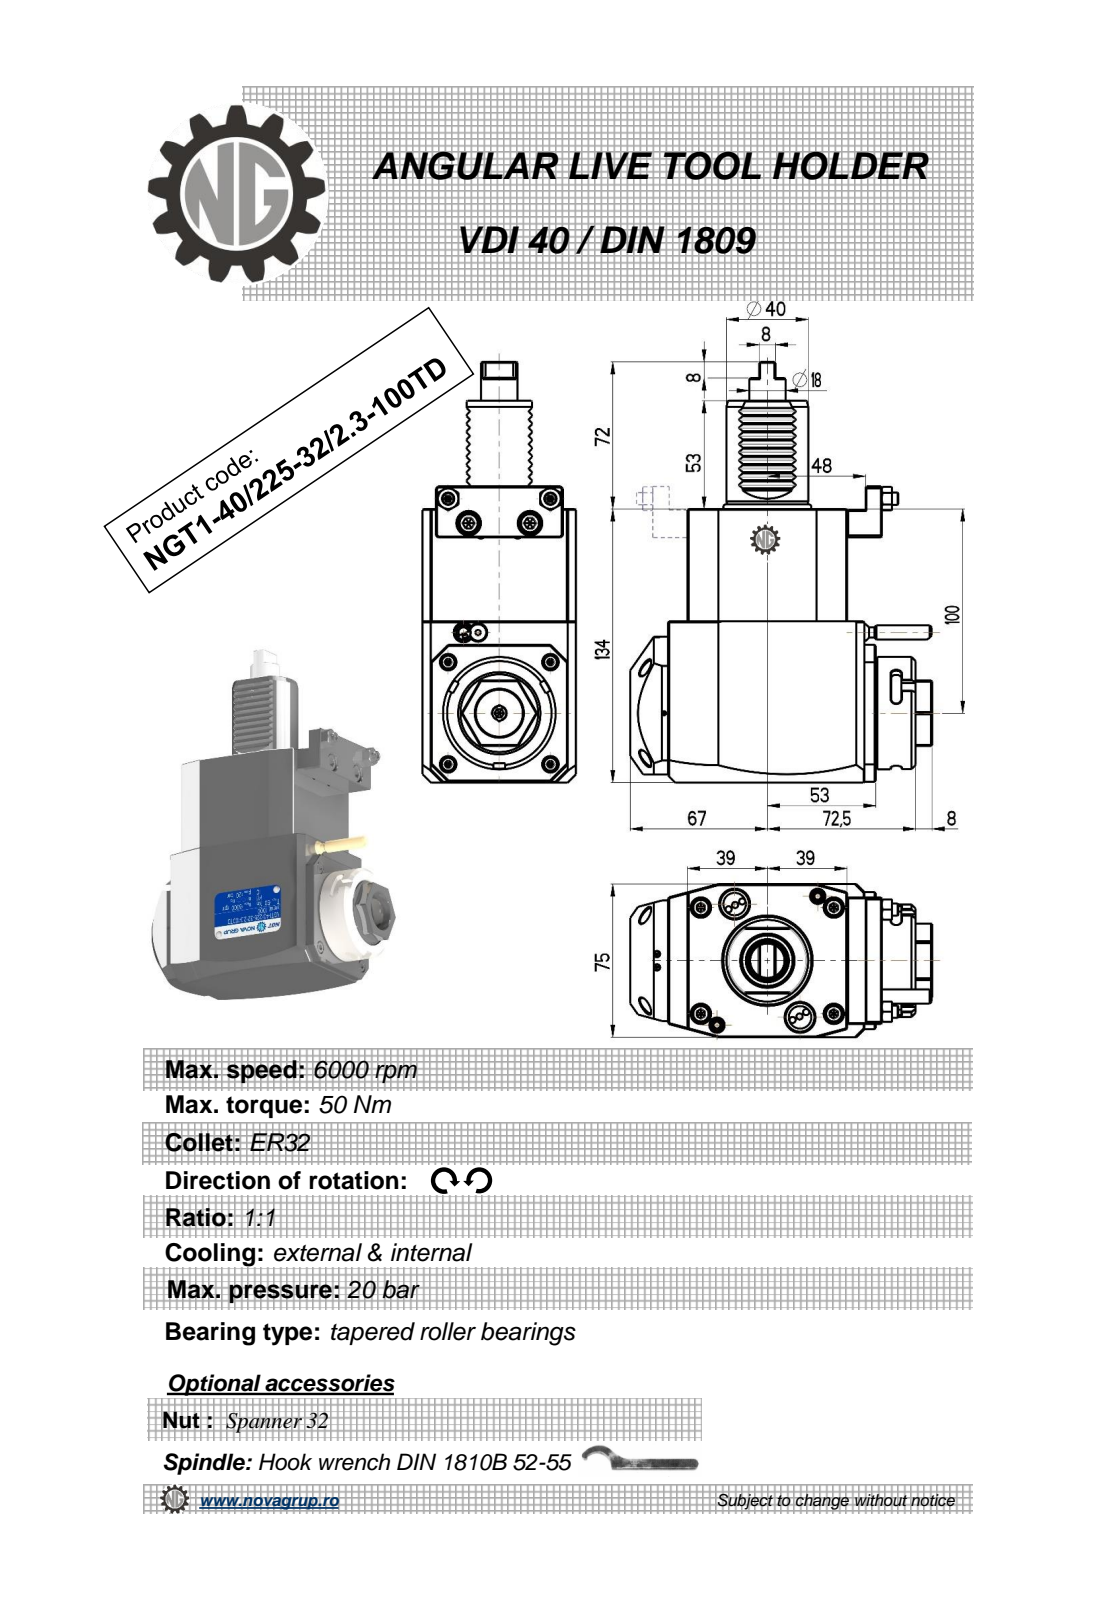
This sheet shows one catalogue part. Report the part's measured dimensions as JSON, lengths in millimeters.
{"part_name": "NGT1_40_225_32_1_3_100TD", "step_written_by": "PRO/ENGINEER BY PARAMETRIC TECHNOLOGY CORPORATION, 2010280 (CONFIG_CONTROL_DESIGN)", "units": "millimeters", "bodies": {"solids": 1, "faces": 380, "planar": 219, "cylindrical": 71, "other": 90}, "overall_size": [206, 147.5, 75], "volume_mm3": 1077000, "surface_area_mm2": 78588, "round_holes": [[2.5, 1], [3, 1], [23, 1]], "round_bosses_or_shafts": [[6, 2], [55, 1], [48, 1], [40, 1], [17.8, 1], [8, 1], [7, 1], [5, 1]], "partial_cylinders_radius": [[0.3, 20], [0.31, 10], [2.5, 6], [0.8, 2], [180, 2], [24.5, 1], [37.5, 1]], "face_to_face_distances": [75, 134, 14, 78, 0.5, 92, 120, 8.5, 19.5, 84.88], "hole_center_spacings": [43.2]}
